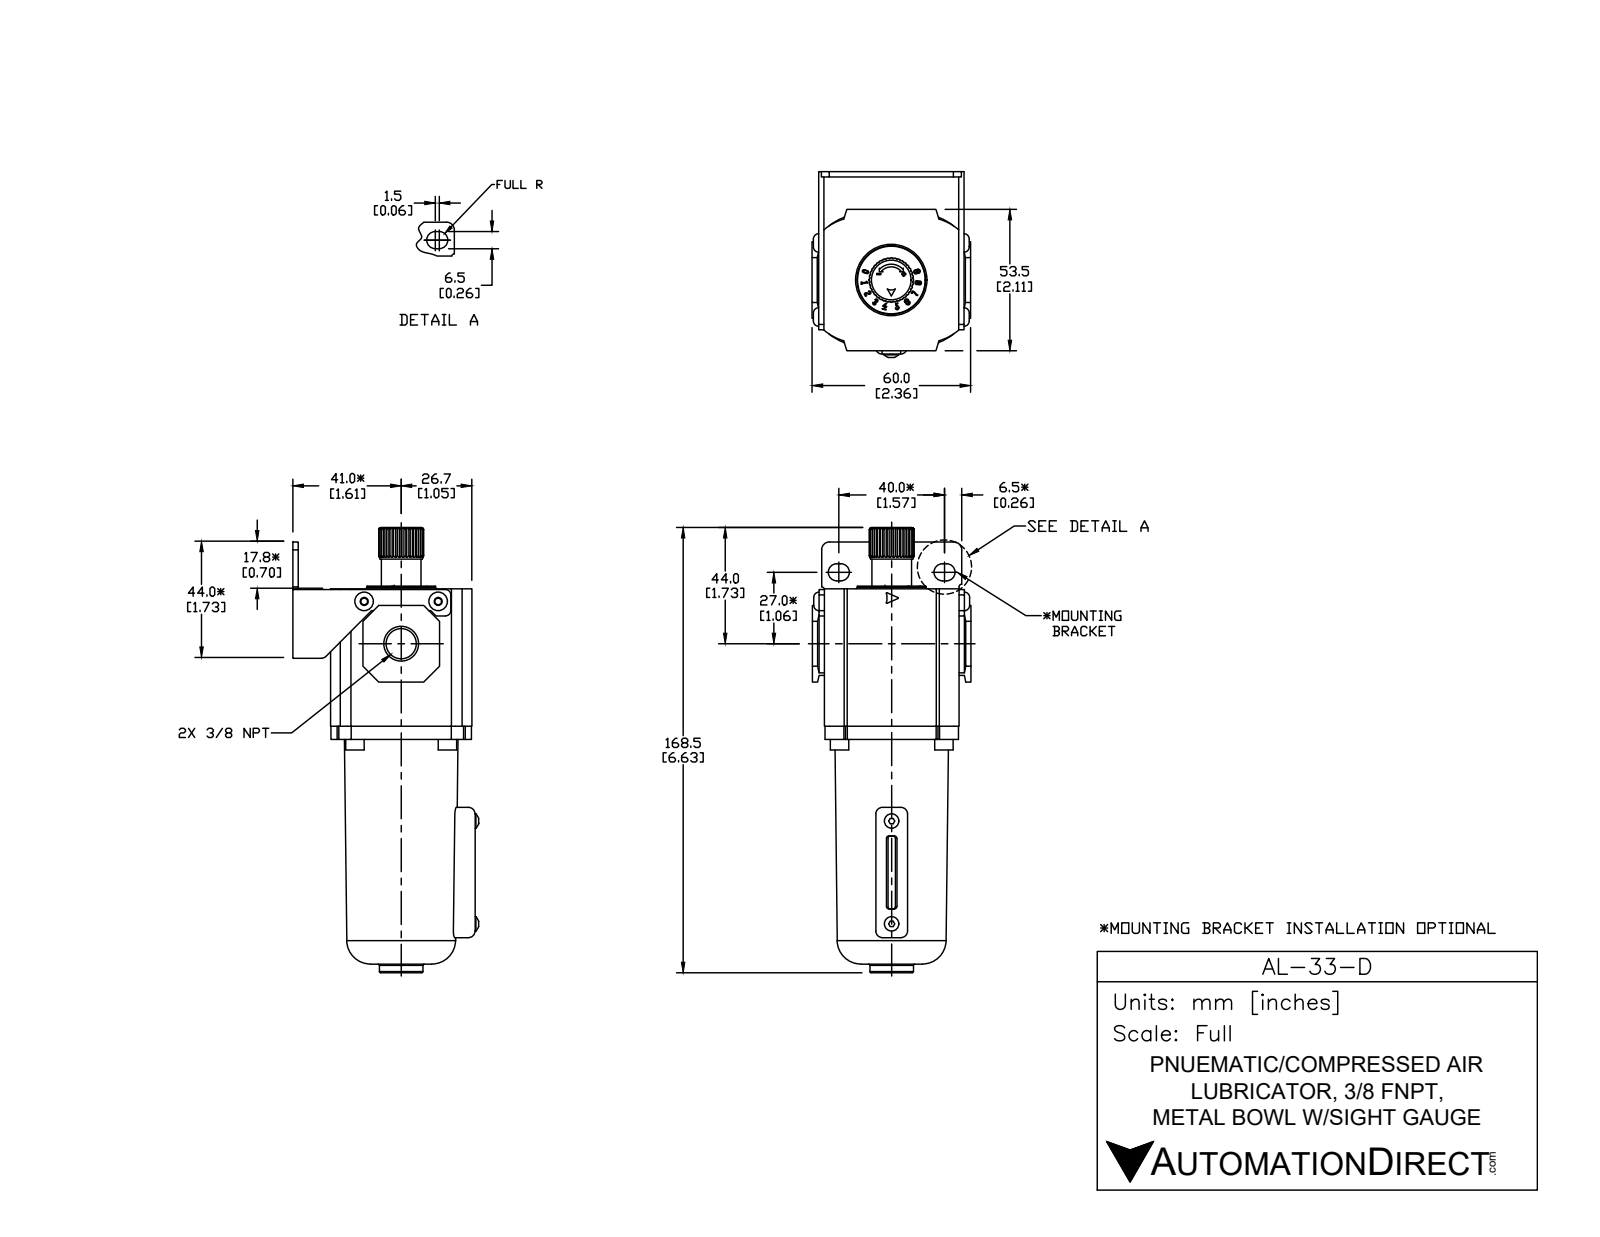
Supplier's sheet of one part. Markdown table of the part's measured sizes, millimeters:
| quantity | value |
| --- | --- |
| part name | AL-33-D |
| STEP written by | SolidWorks 2015 (CONFIG_CONTROL_DESIGN) |
| units | millimeters |
| bodies | 7 solids, 575 faces (335 planar, 110 cylindrical, 130 other) |
| overall size | 168.5 × 71 × 60 |
| volume | 276 143 mm³ |
| surface area | 47 752 mm² |
| round holes (diameter × count) | 3.4 × 2, 14.27 × 1 |
| round bosses / shafts (diameter × count) | 7 × 4, 5.5 × 2, 26 × 1, 16.5 × 1, 15 × 1 |
| partial cylindrical surfaces (radius × count) | 1.3 × 8, 2.5 × 8, 2 × 5, 0.3 × 4, 1 × 4, 3.25 × 4, 19.9 × 4, 20 × 4 |
| main face-to-face distances | 2, 53, 52, 53.4, 12.3, 14.3, 67.7, 65.7, 51, 2.5 |
| hole center spacings | 21.06, 21.46, 28 |
